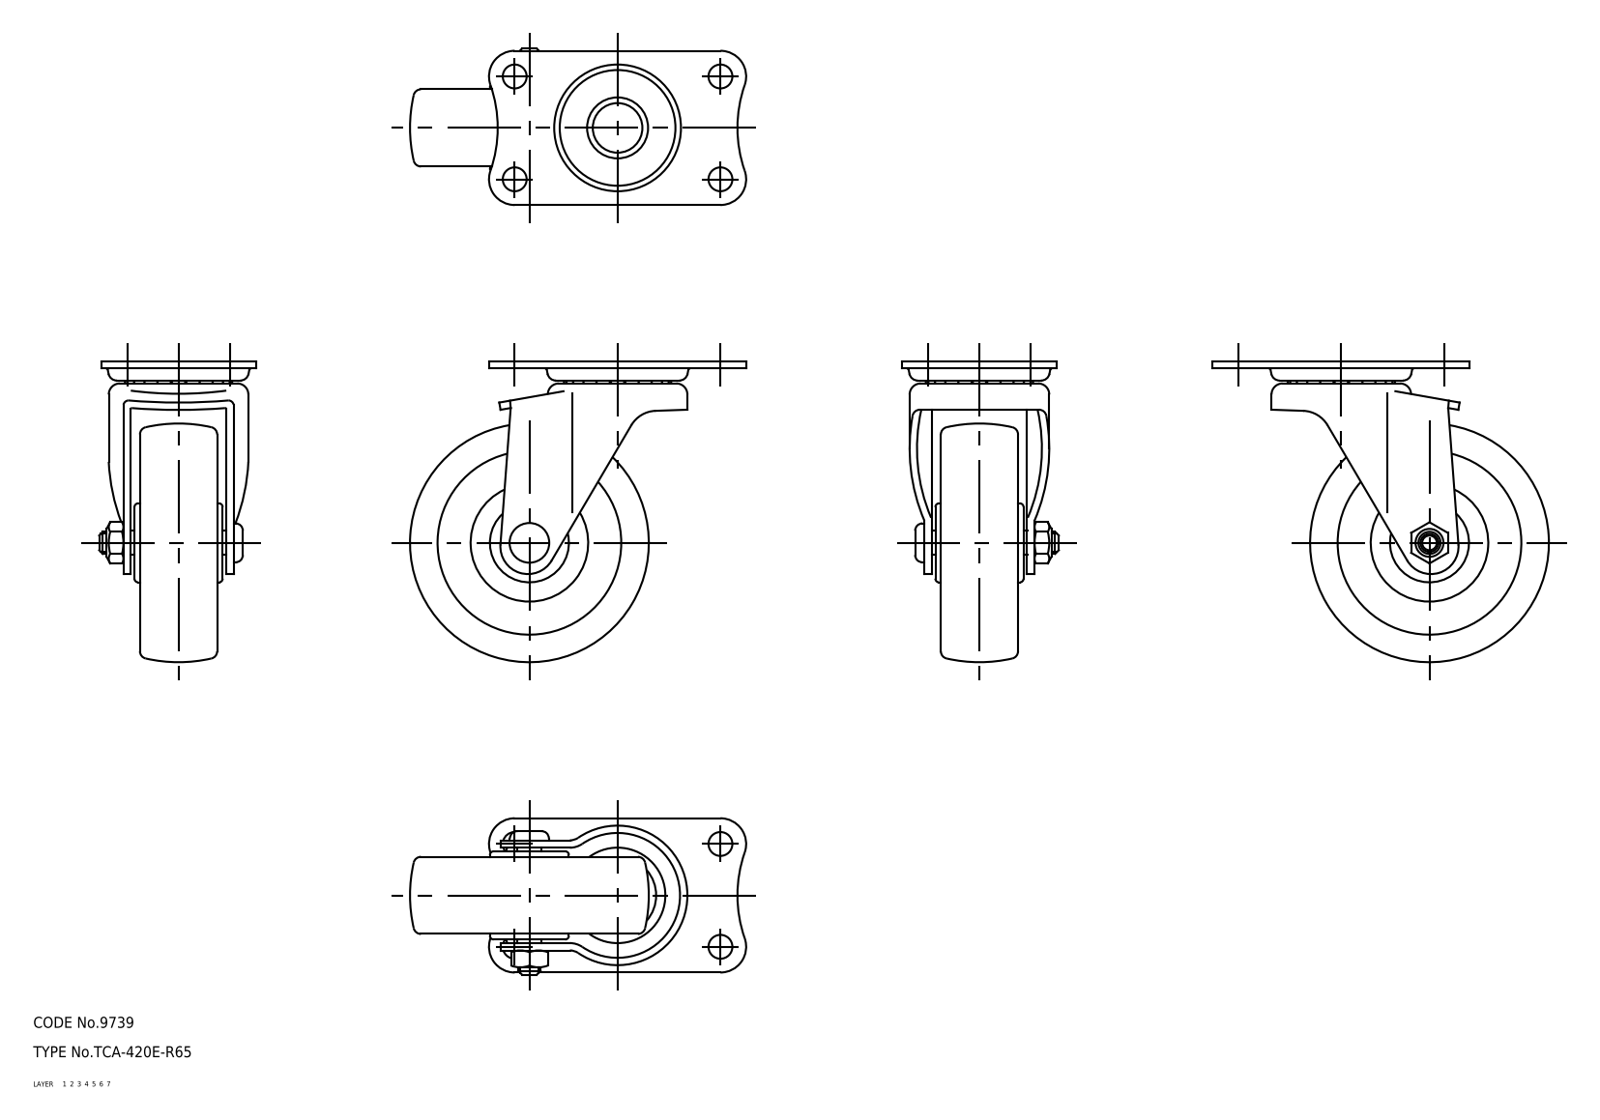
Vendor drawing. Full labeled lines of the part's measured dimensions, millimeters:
Part name (STEP PRODUCT): 67135014; 67135027; 67135040; 67135053 (+1 more)
STEP written by: CADfix (AUTOMOTIVE_DESIGN)
Units: millimetres
Bodies: 5 solids, 235 faces (0 planar, 0 cylindrical, 235 other)
Overall size (bounding box): 91.5 × 82 × 42.6
Volume: 85 030 mm³ · Surface area: 29 673 mm²
